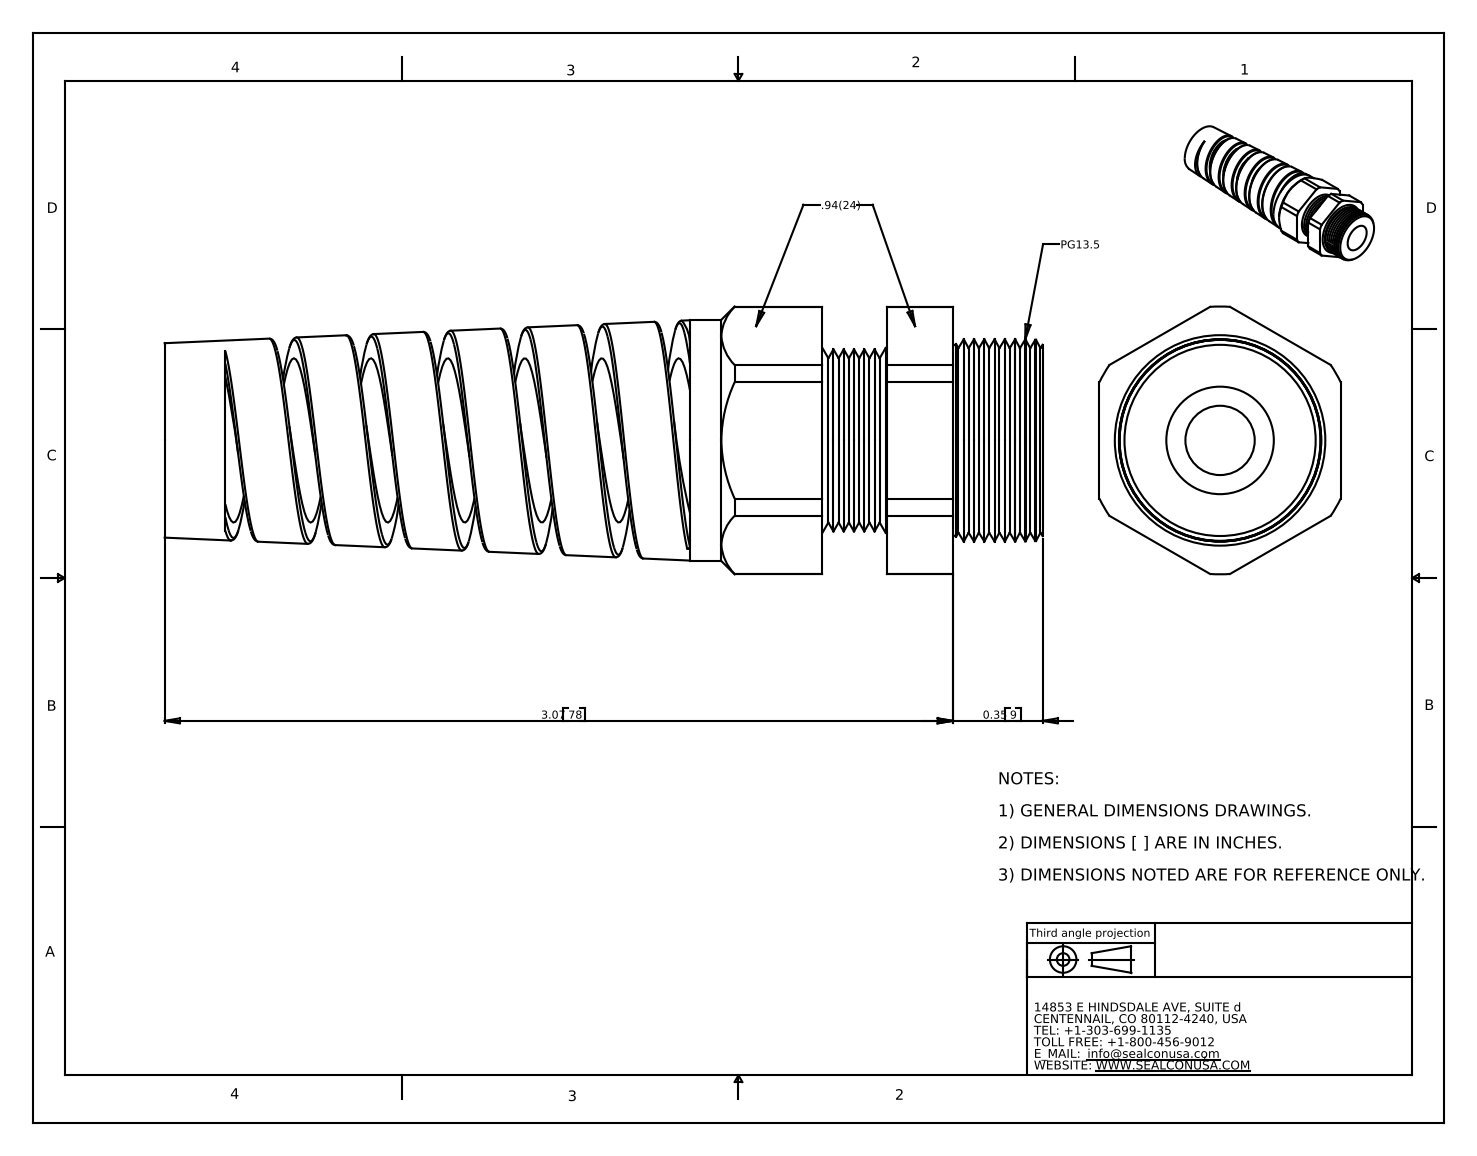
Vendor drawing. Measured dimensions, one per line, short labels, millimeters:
name: CF13BR-BK
written by: SolidWorks 2007 (CONFIG_CONTROL_DESIGN)
unit: mm
bodies: 2 solids, 161 faces (24 planar, 37 cylindrical, 100 other)
size: 86.9 × 26.5 × 23.9
volume: 17 440 mm³; area: 13 450 mm²
holes: 1× ⌀6.9, 1× ⌀16.3
bosses: 1× ⌀23.9, 1× ⌀18.3
rounds: 1× R8.4, 1× R13.3
face distances: 23.9, 6.4, 21.8, 15.4, 12.9, 6.5, 8.9, 11.2, 17.6, 24.1
